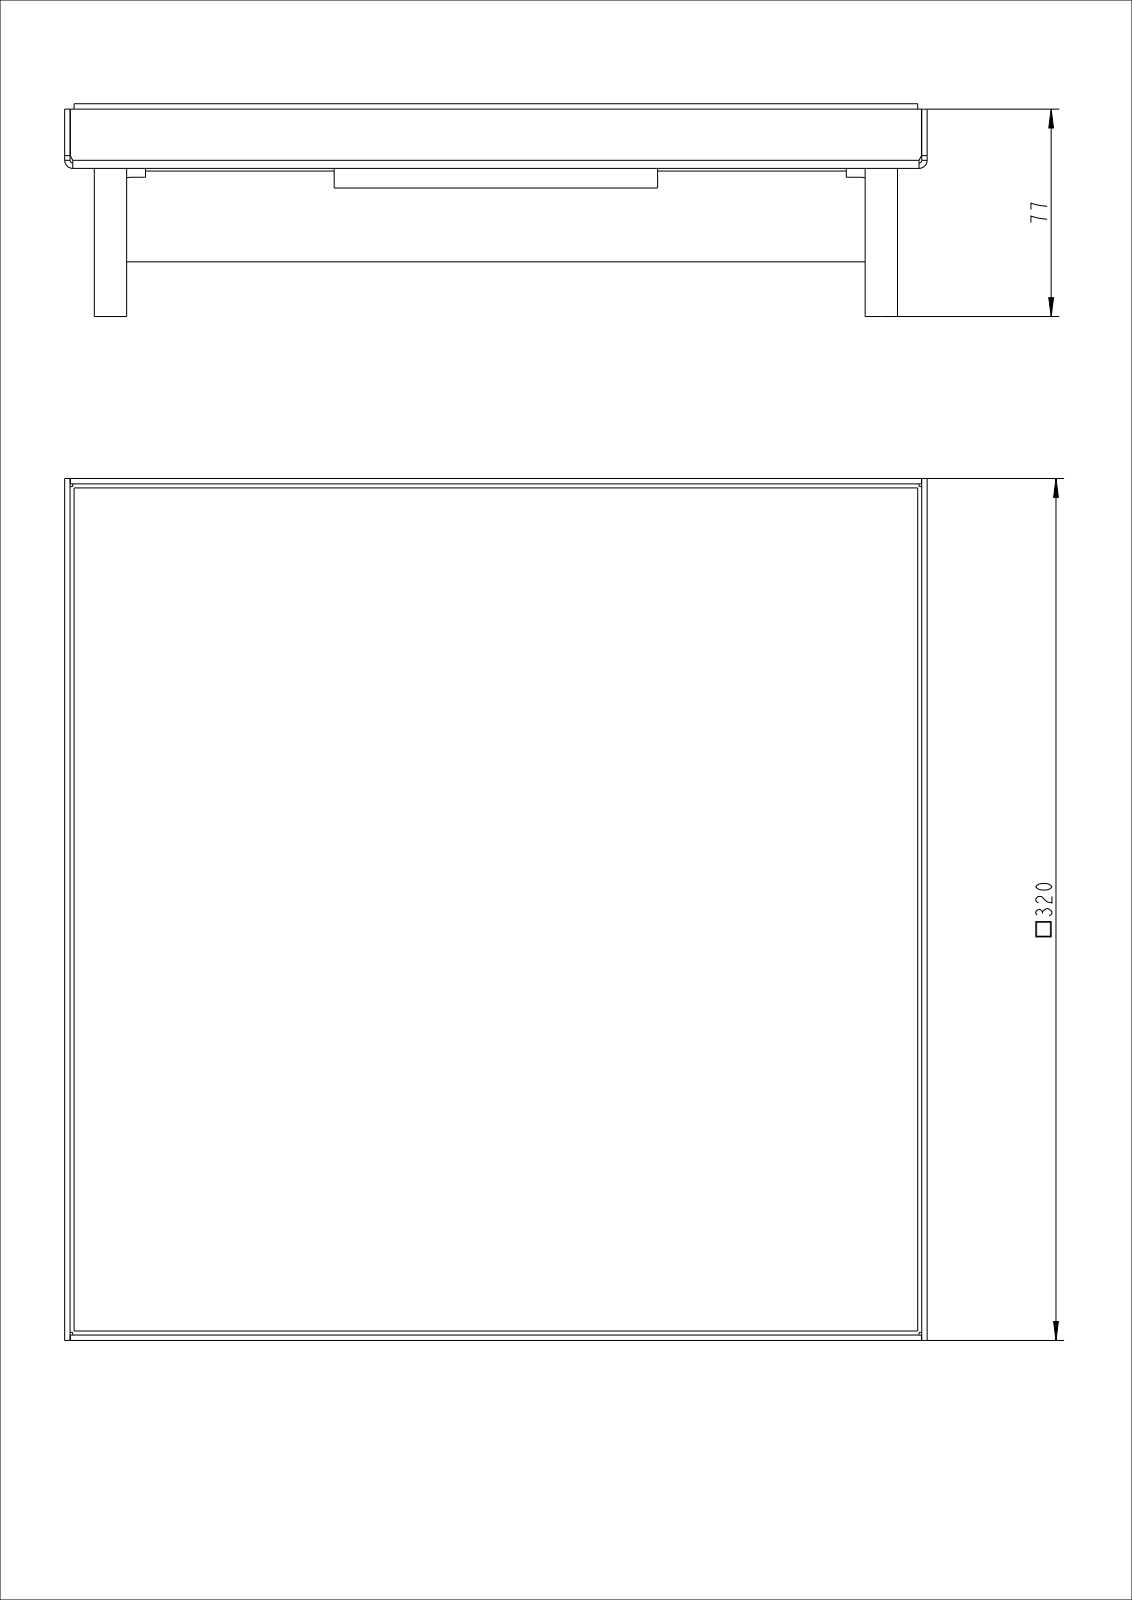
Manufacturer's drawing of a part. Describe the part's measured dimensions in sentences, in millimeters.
The part is named "T-00644; U09001; T-00959; T-00835_ASM". Its 3-D file was written by "CREO PARAMETRIC BY PTC INC, 2022024 (AUTOMOTIVE_DESIGN)". It is 2 solids with 148 faces: 104 planar, 44 cylindrical and 0 other. Overall it measures 320 by 320 by 79 millimeters. Its volume is 2 298 000 cubic millimeters and its surface area 382 462 square millimeters. Round bosses or shafts: 4 of diameter 12, 4 of diameter 9.85. Partial cylindrical surfaces (rounded edges, fillets, slot ends): 6 of radius 1, 6 of radius 3, 6 of radius 10, 2 of radius 5. The main face-to-face distances are 22, 2, 24, 3.5, 316.5, 318, 1.5, 314.5, 45.3, 272.7.
